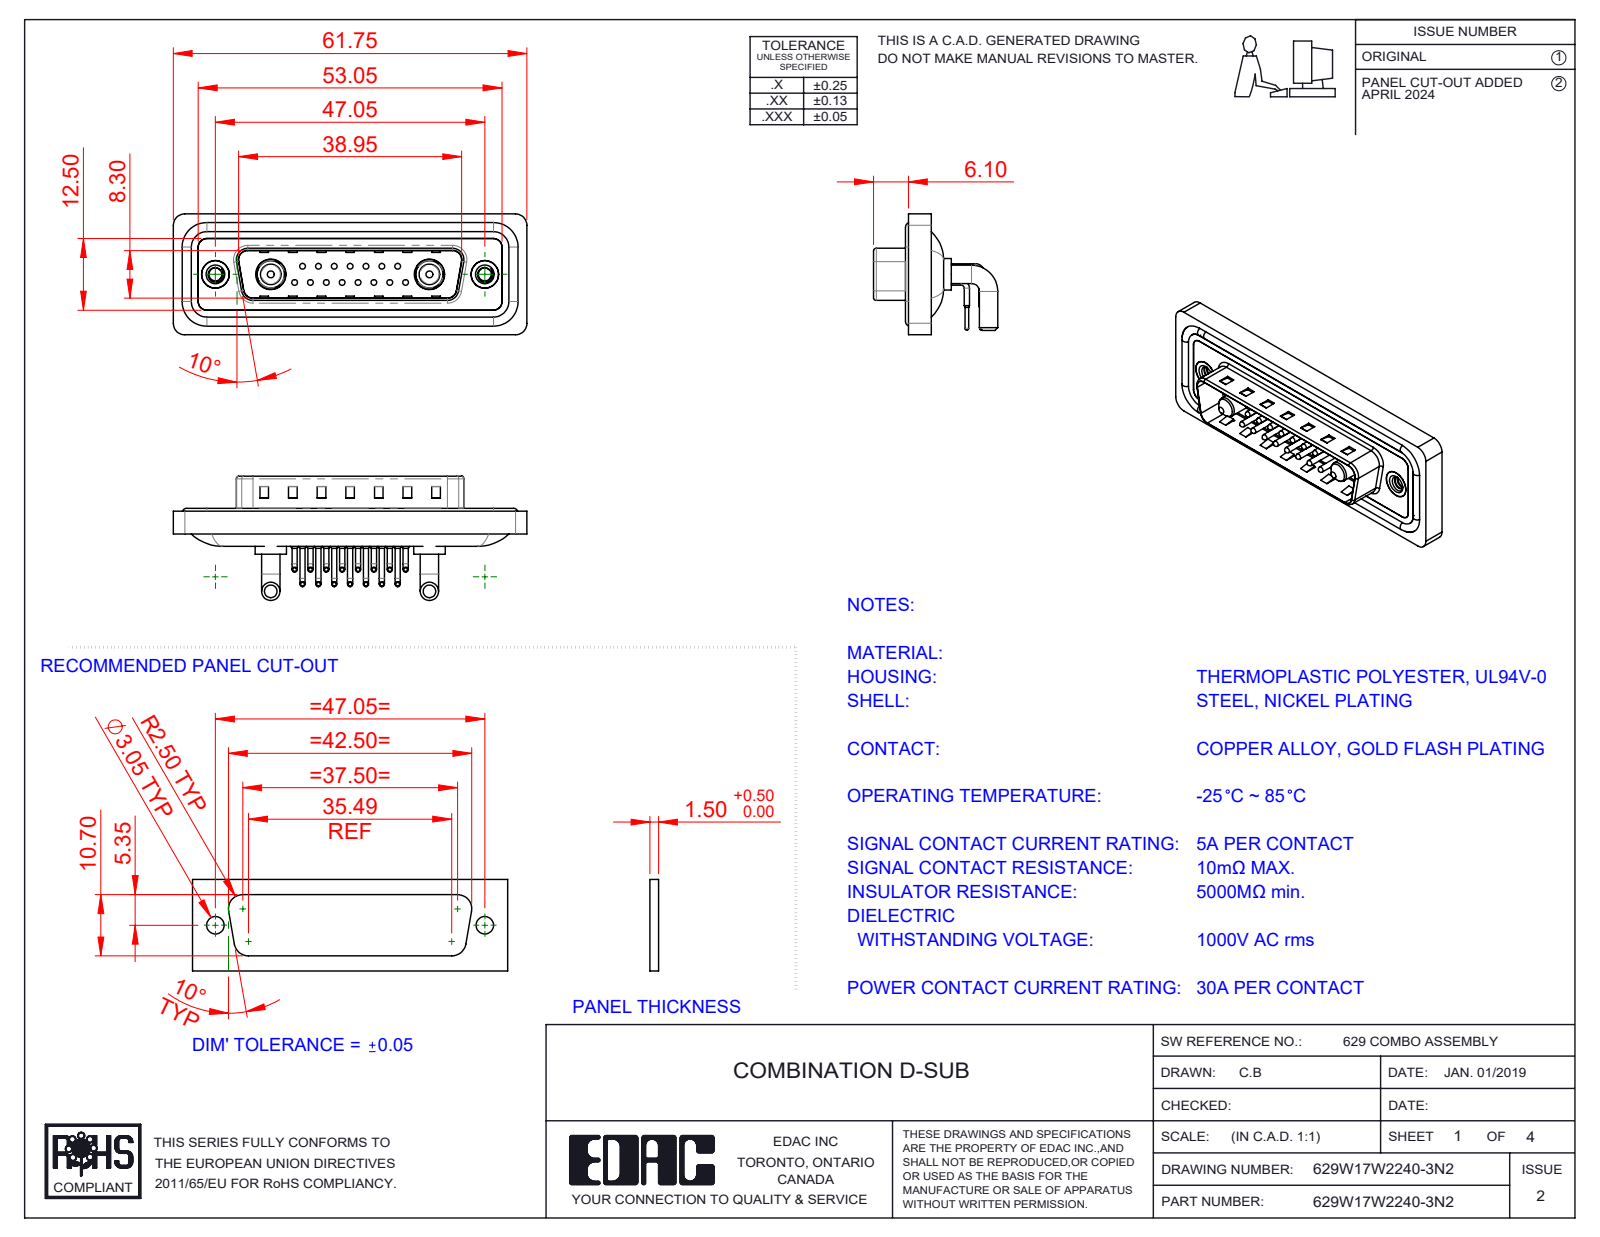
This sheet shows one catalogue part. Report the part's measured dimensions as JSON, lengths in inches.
{"part_name": "629Combo Threaded Rivet_2; 629W17W2240-3N2; 629Combo Waterproof Housing_25 Contacts; 629Combo Contact Row 1 (+5 more)", "step_written_by": "SolidWorks 2023 (CONFIG_CONTROL_DESIGN)", "units": "inches", "bodies": {"solids": 26, "faces": 2219, "planar": 1189, "cylindrical": 770, "other": 260}, "overall_size": [2.431, 0.854, 0.831], "volume_in3": 0.462, "surface_area_in2": 19.59, "round_holes": [[0.03, 15], [0.063, 15], [0.079, 15], [0.089, 2], [0.157, 2], [0.189, 2], [0.191, 2], [0.197, 2], [0.209, 2]], "round_bosses_or_shafts": [[0.035, 30], [0.059, 15], [0.039, 15], [0.026, 15], [0.126, 4], [0.063, 4], [0.217, 2], [0.205, 2]], "partial_cylinders_radius": [[0.059, 18], [0.079, 18], [0.04, 15], [0.02, 8], [0.063, 8], [0.01, 4], [0.024, 4], [0.026, 4]], "face_to_face_distances": [0.016, 0.114, 0.031, 0.161, 0.043, 0.083, 0.063, 0.177, 0.059, 0.098], "hole_center_spacings": [0.124, 0.109, 0.218, 0.327, 0.198, 0.295, 0.436, 0.198]}
